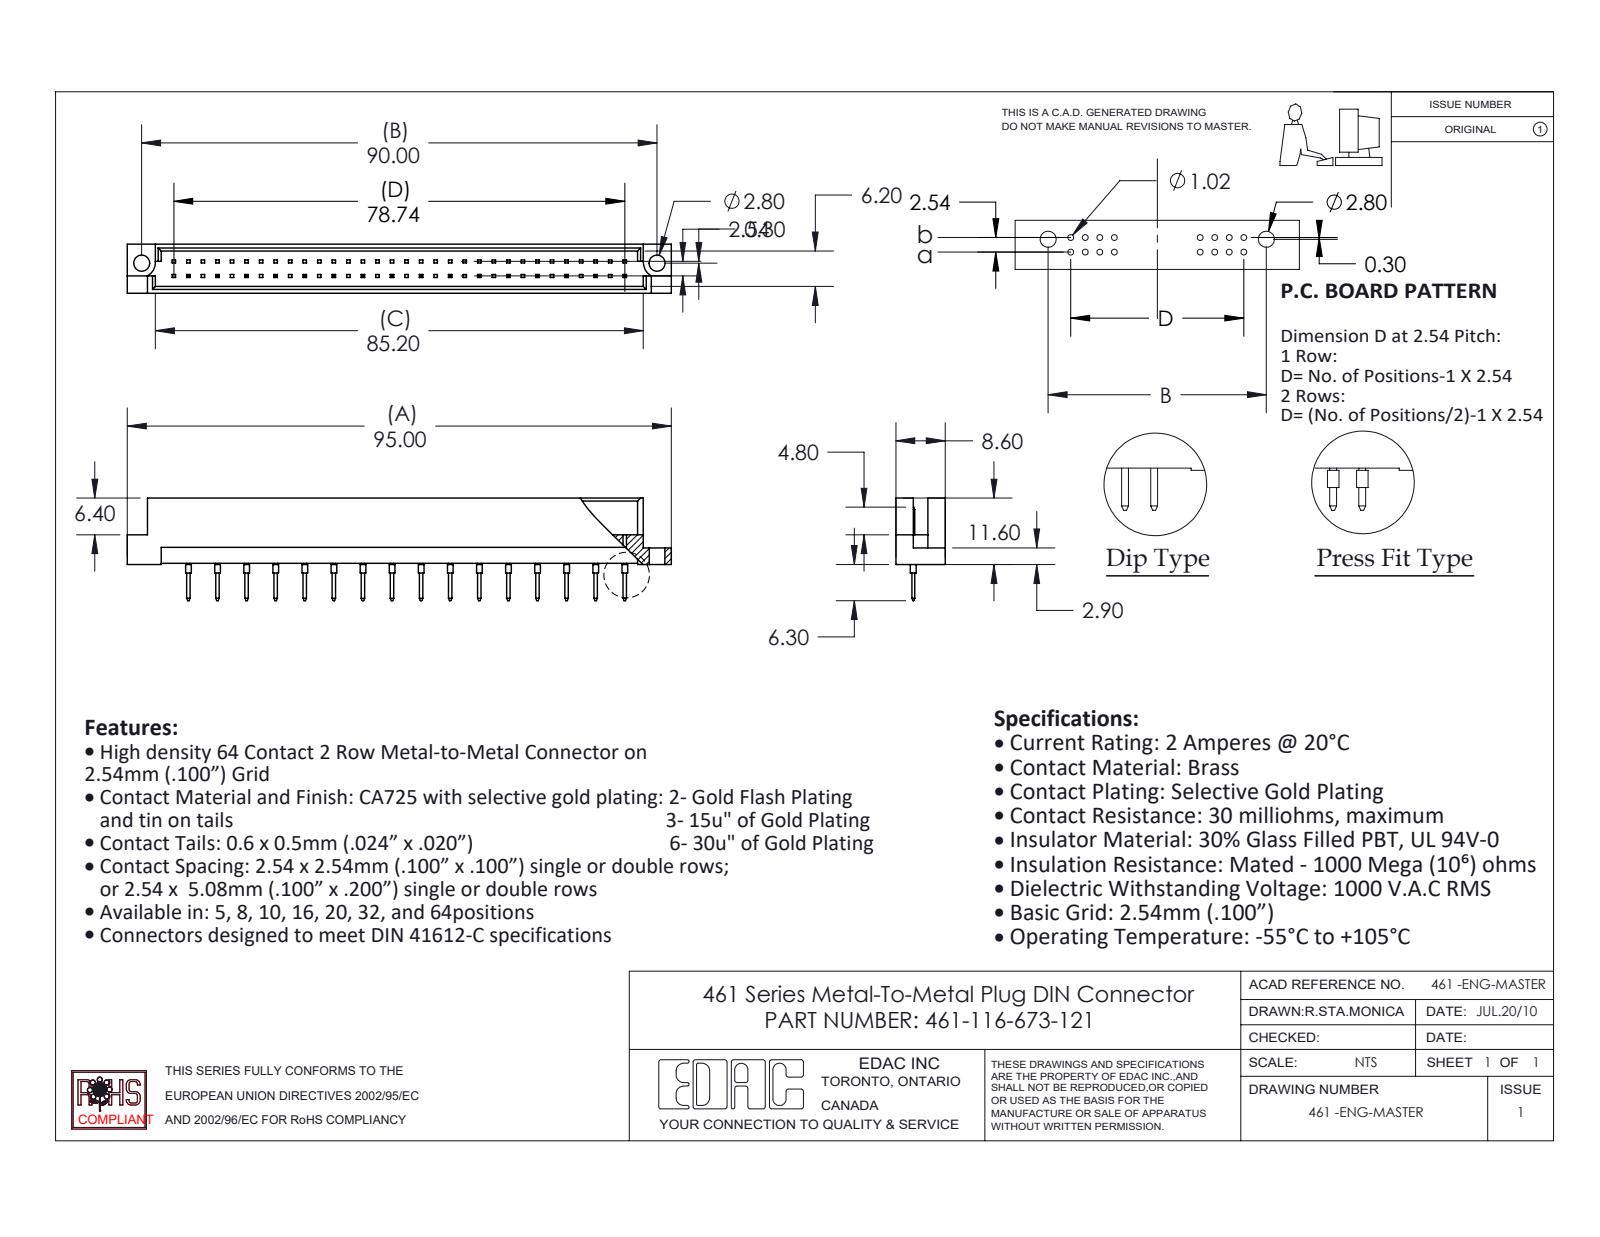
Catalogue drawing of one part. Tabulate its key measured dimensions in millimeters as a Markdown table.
| quantity | value |
| --- | --- |
| part name | 461-116-673-121; 461 Part_64; 461-290_73 |
| STEP written by | SolidWorks 2020 (CONFIG_CONTROL_DESIGN) |
| units | millimeters |
| bodies | 17 solids, 657 faces (618 planar, 39 cylindrical, 0 other) |
| overall size | 95 × 17.9 × 8.6 |
| volume | 4 745 mm³ |
| surface area | 6 278 mm² |
| round holes (diameter × count) | 2.8 × 2 |
| round bosses / shafts (diameter × count) | 1 × 16 |
| partial cylindrical surfaces (radius × count) | 2.8 × 2 |
| main face-to-face distances | 1.2, 7.4, 8.6, 6.2, 5, 3.28, 5.32, 2.08, 4.12, 2.78 |
| hole center spacings | 90 |
